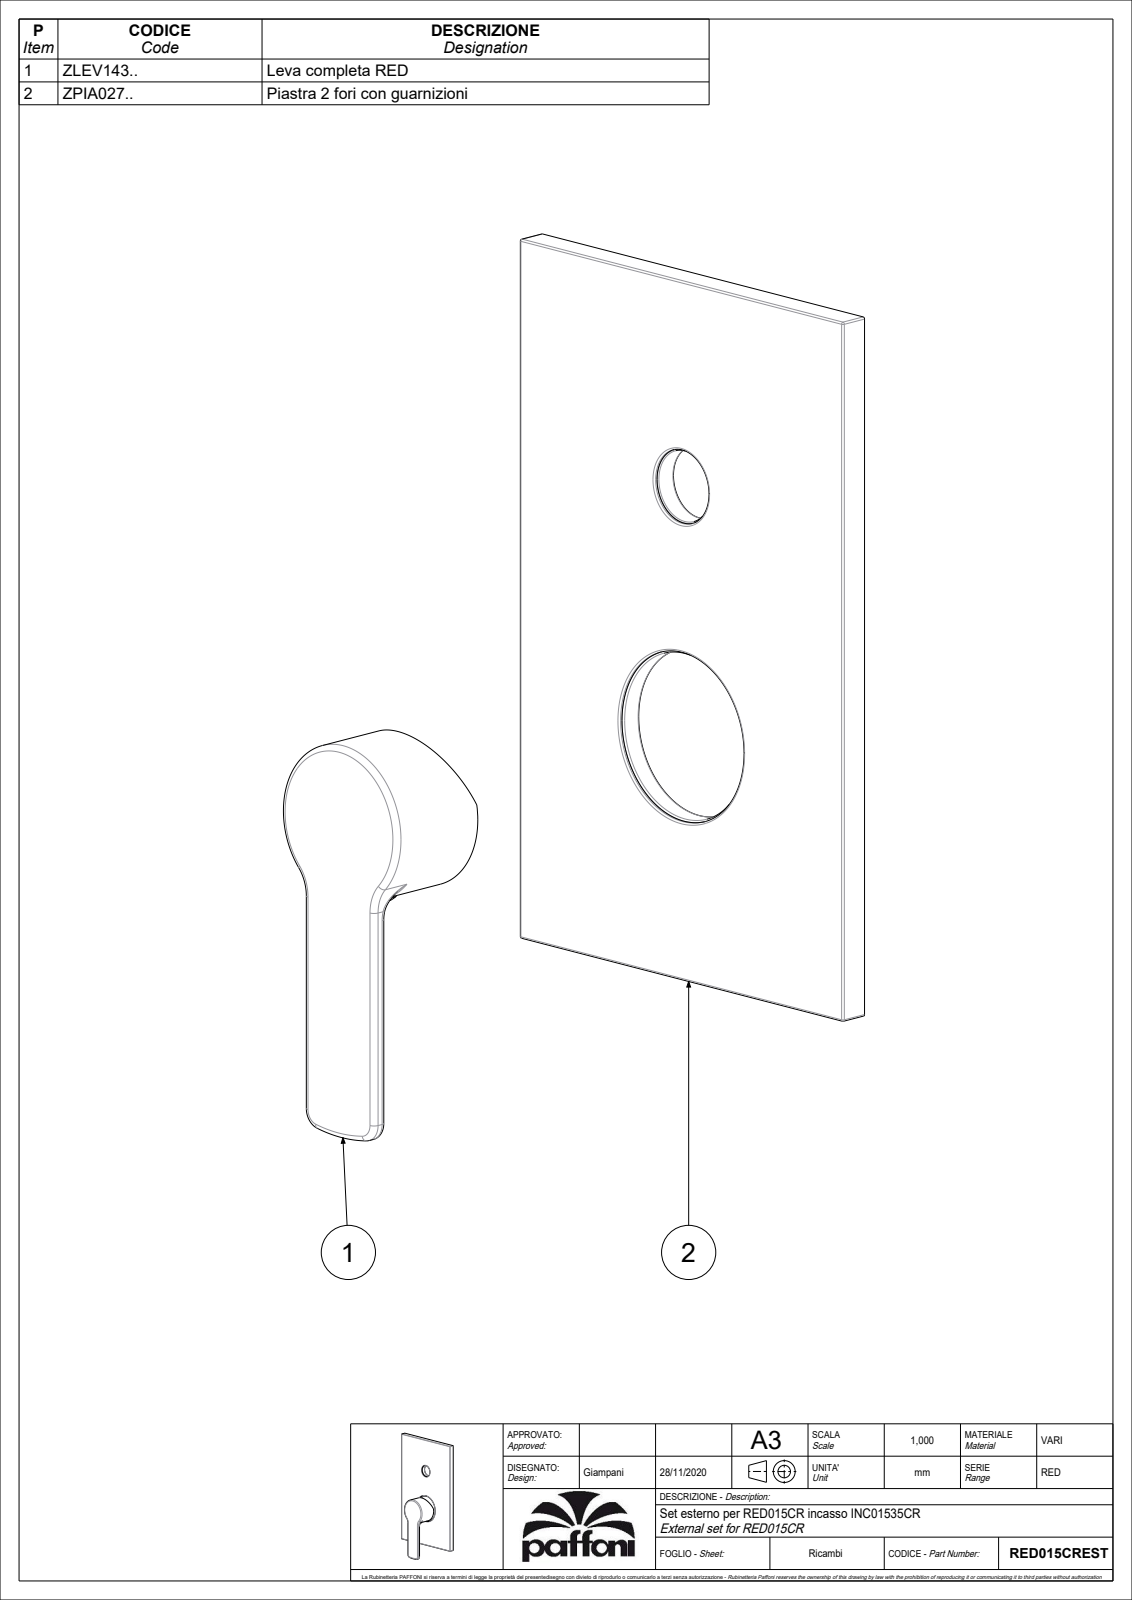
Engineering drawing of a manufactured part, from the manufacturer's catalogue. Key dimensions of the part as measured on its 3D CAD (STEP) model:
Part name (STEP PRODUCT): RED015CREST
STEP written by: CREO PARAMETRIC BY PTC INC, 2020044 (CONFIG_CONTROL_DESIGN)
Units: millimetres
Bodies: 2 solids, 317 faces (87 planar, 113 cylindrical, 117 other)
Overall size (bounding box): 209 × 120 × 40.23
Volume: 136 601 mm³ · Surface area: 69 814 mm²
Round holes (diameter × count): ⌀3 ×1, ⌀3.3 ×1, ⌀4.5 ×1, ⌀19.2 ×1, ⌀20 ×1, ⌀23.2 ×1, ⌀45 ×1, ⌀46 ×1
Round bosses / shafts (diameter × count): ⌀51 ×1, ⌀49 ×1, ⌀43 ×1, ⌀25 ×1, ⌀23 ×1, ⌀7.6 ×1, ⌀5.5 ×1, ⌀5 ×1
Partial cylindrical surfaces — rounded edges, fillets, slot ends (radius × count): R0.5 ×47, R1 ×8, R1.5 ×4, R5 ×2, R10 ×2, R50 ×1
Main face-to-face distances: 7.5, 2.5, 5, 0.5, 22.5, 34.5, 30, 35, 4.5, 27.5
Hole centre spacings: 68
